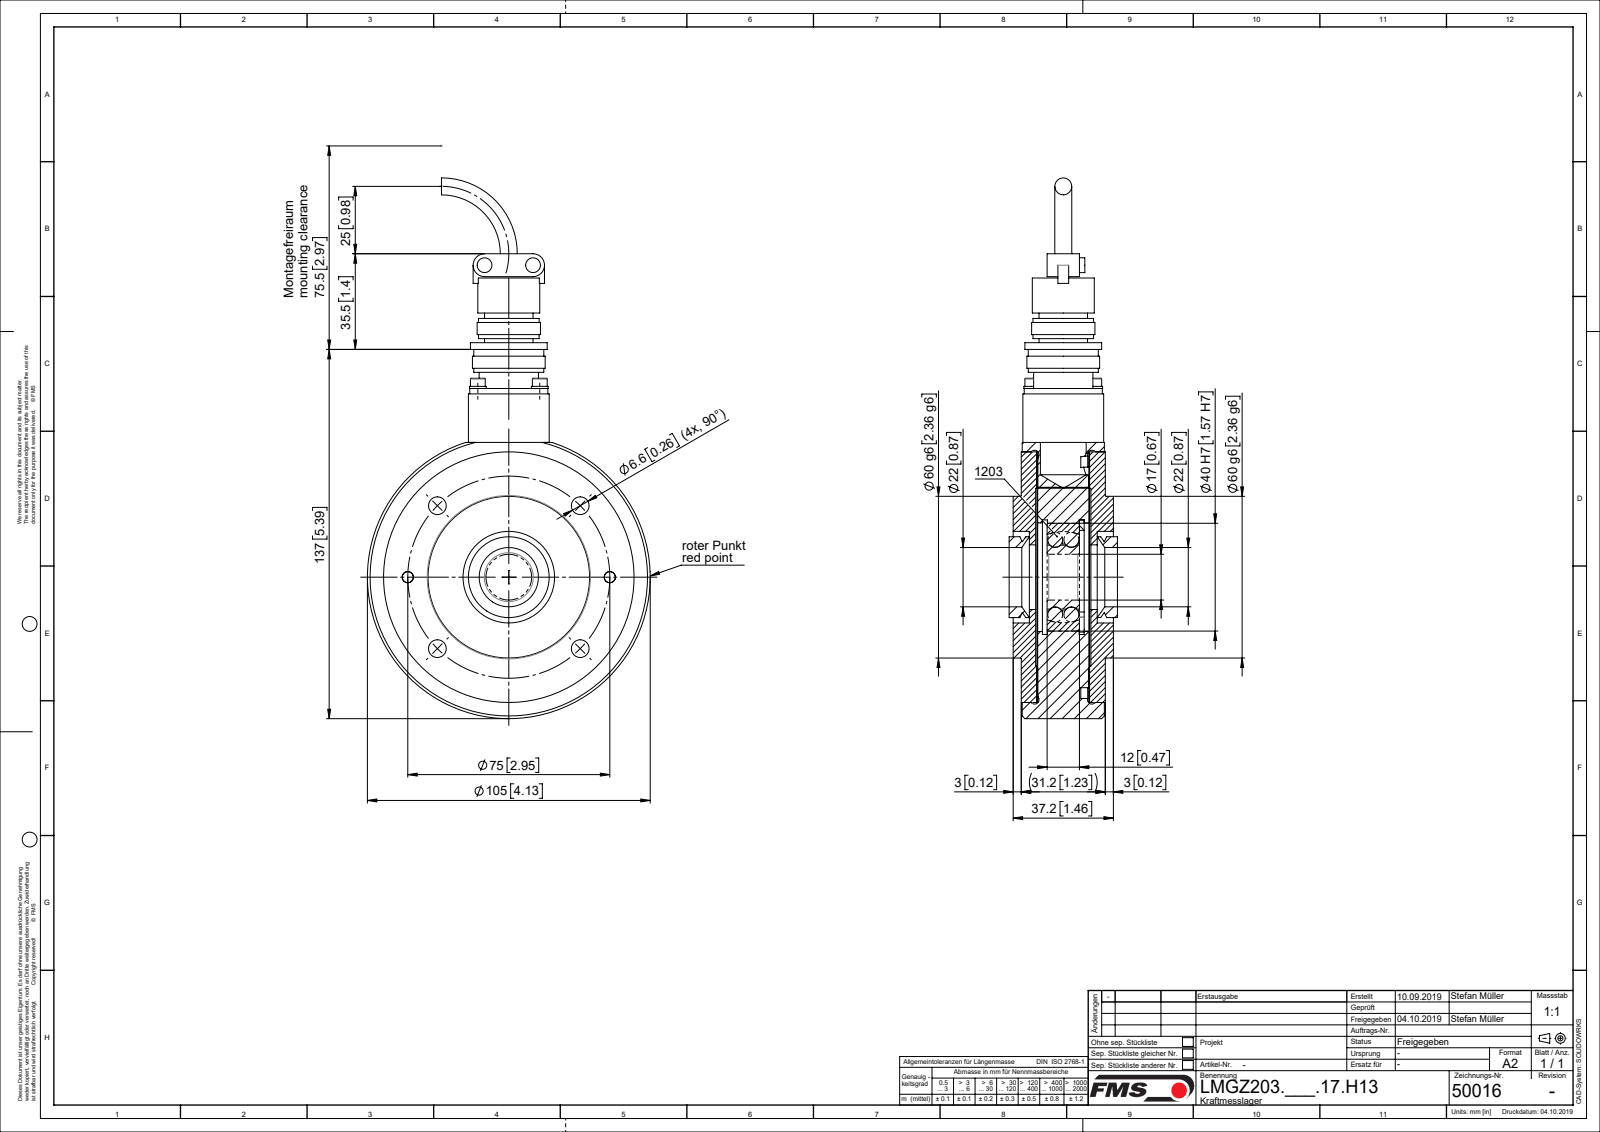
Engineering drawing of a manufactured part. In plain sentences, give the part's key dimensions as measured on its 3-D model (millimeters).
The part is named "ZEICHNUNG3; L50016; L4795904; L47958(1) (+8 more)". Its 3-D file was written by "Mechanical Desktop 2007 (CONFIG_CONTROL_DESIGN)". It is 21 solids with 401 faces: 116 planar, 233 cylindrical and 52 other. Overall it measures 200.65 by 105 by 37.2 millimeters. Its volume is 288 145 cubic millimeters and its surface area 104 822 square millimeters. Round holes: 4 of diameter 2.6, 4 of diameter 3.2, 4 of diameter 3.4, 4 of diameter 6.6, 2 of diameter 4, 2 of diameter 5.3, 2 of diameter 5.5, 2 of diameter 10, 1 of diameter 17, 1 of diameter 22, 1 of diameter 23, 1 of diameter 24. Round bosses or shafts: 6 of diameter 5.5, 4 of diameter 6.2, 4 of diameter 3, 4 of diameter 2.5, 2 of diameter 8, 2 of diameter 5, 1 of diameter 105, 1 of diameter 93. Partial cylindrical surfaces (rounded edges, fillets, slot ends): 2 of radius 4.25, 1 of radius 2. The main face-to-face distances are 19.25, 19, 5.85, 6.1, 25.1, 25.35, 20, 19.5, 0.5, 5.35. The hole center spacings are 37.5, 16.26, 23, 28.7, 53.04, 69.3, 32.53, 75.01.
